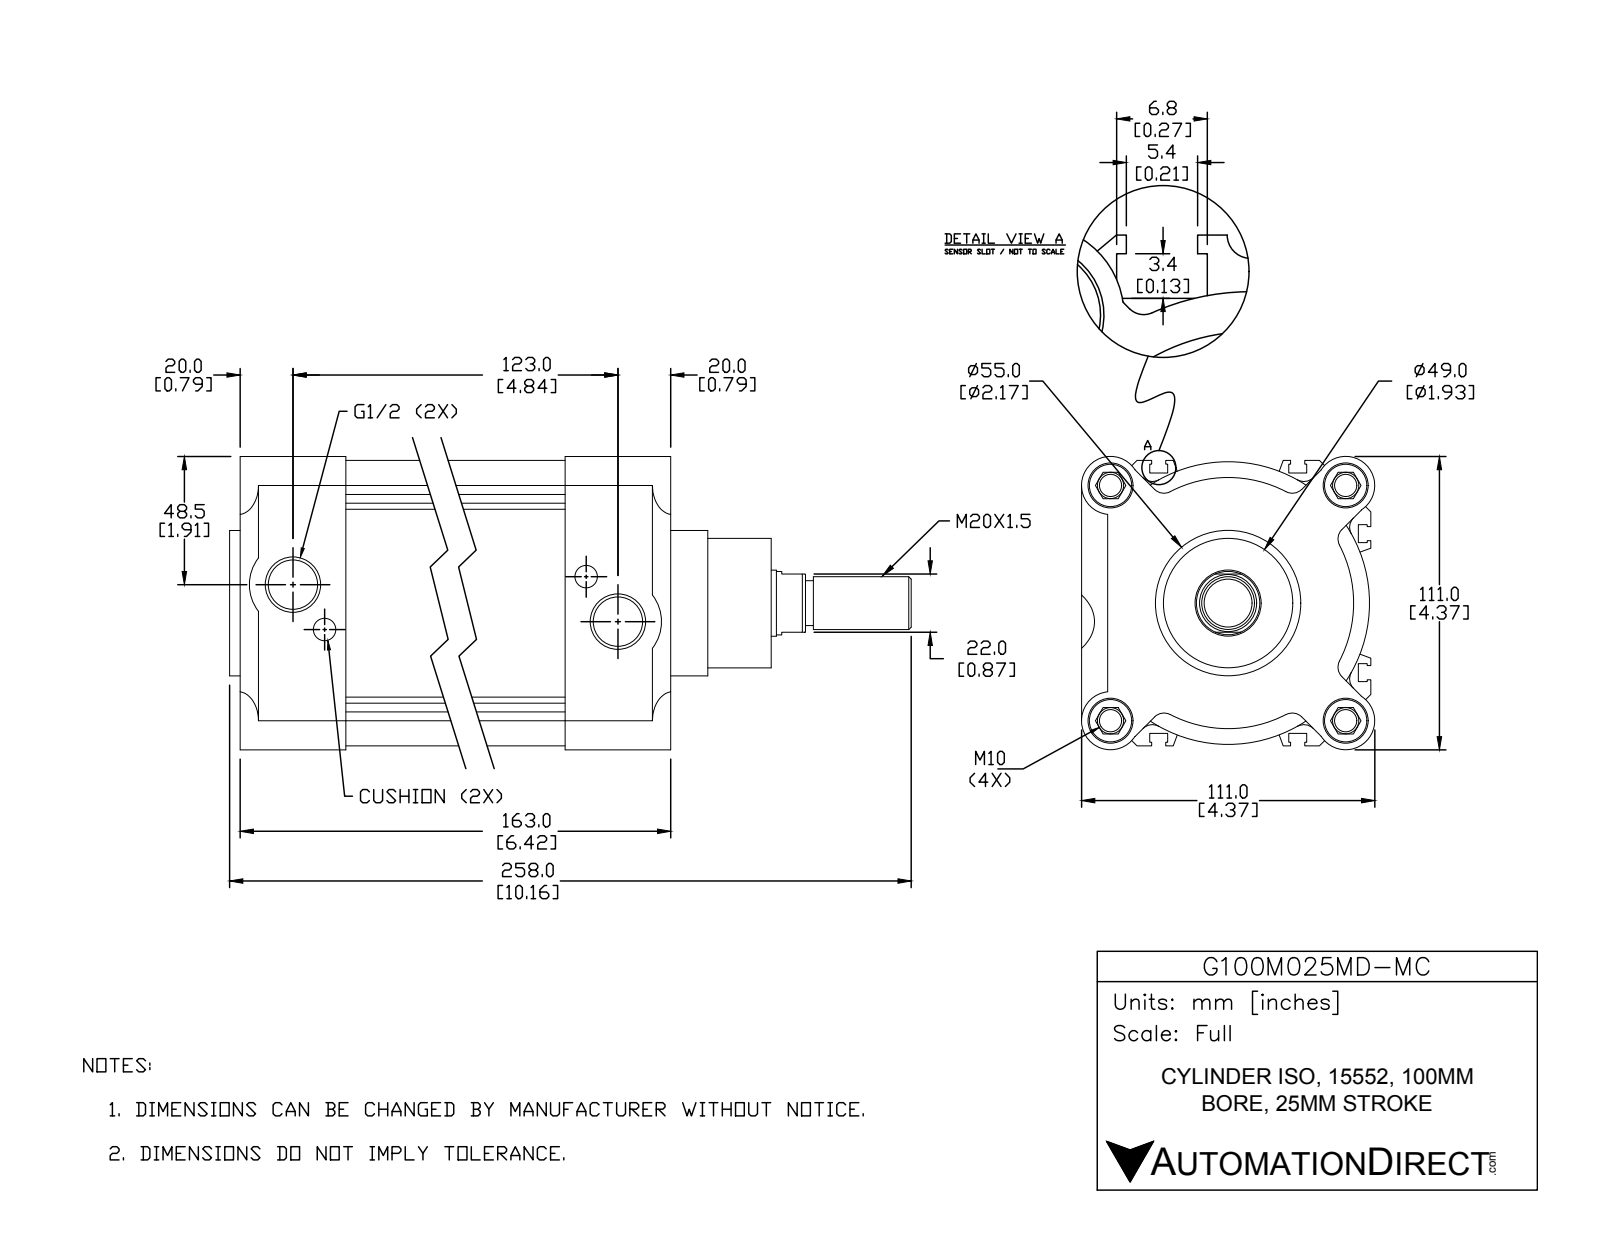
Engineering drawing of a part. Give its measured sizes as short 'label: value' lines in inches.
name: 100-HL; 10012125-R; 100-25-120.5-B; G100M025MD-MC (+1 more)
written by: SolidWorks 2015 (CONFIG_CONTROL_DESIGN)
unit: in
bodies: 4 solids, 462 faces (248 planar, 162 cylindrical, 52 other)
size: 10.157 × 4.37 × 4.37
volume: 100.3 in³; area: 377.2 in²
holes: 4× ⌀0.33, 4× ⌀0.669, 2× ⌀0.335, 2× ⌀0.734, 1× ⌀0.984
bosses: 4× ⌀0.63, 1× ⌀3.937, 1× ⌀2.165, 1× ⌀1.929, 1× ⌀0.945, 1× ⌀0.787, 1× ⌀0.669
rounds: 12× R0.197, 6× R0.004, 4× R0.374, 4× R0.433, 2× R0.65, 1× R1.87, 1× R2.087, 1× R2.106
face distances: 4.449, 0.394, 2.874, 1.575, 1.969, 4.843, 1.496, 3.465, 2.48, 0.984
hole spacings: 2.478, 3.504, 0.819, 4.372, 4.956, 3.976, 4.874
